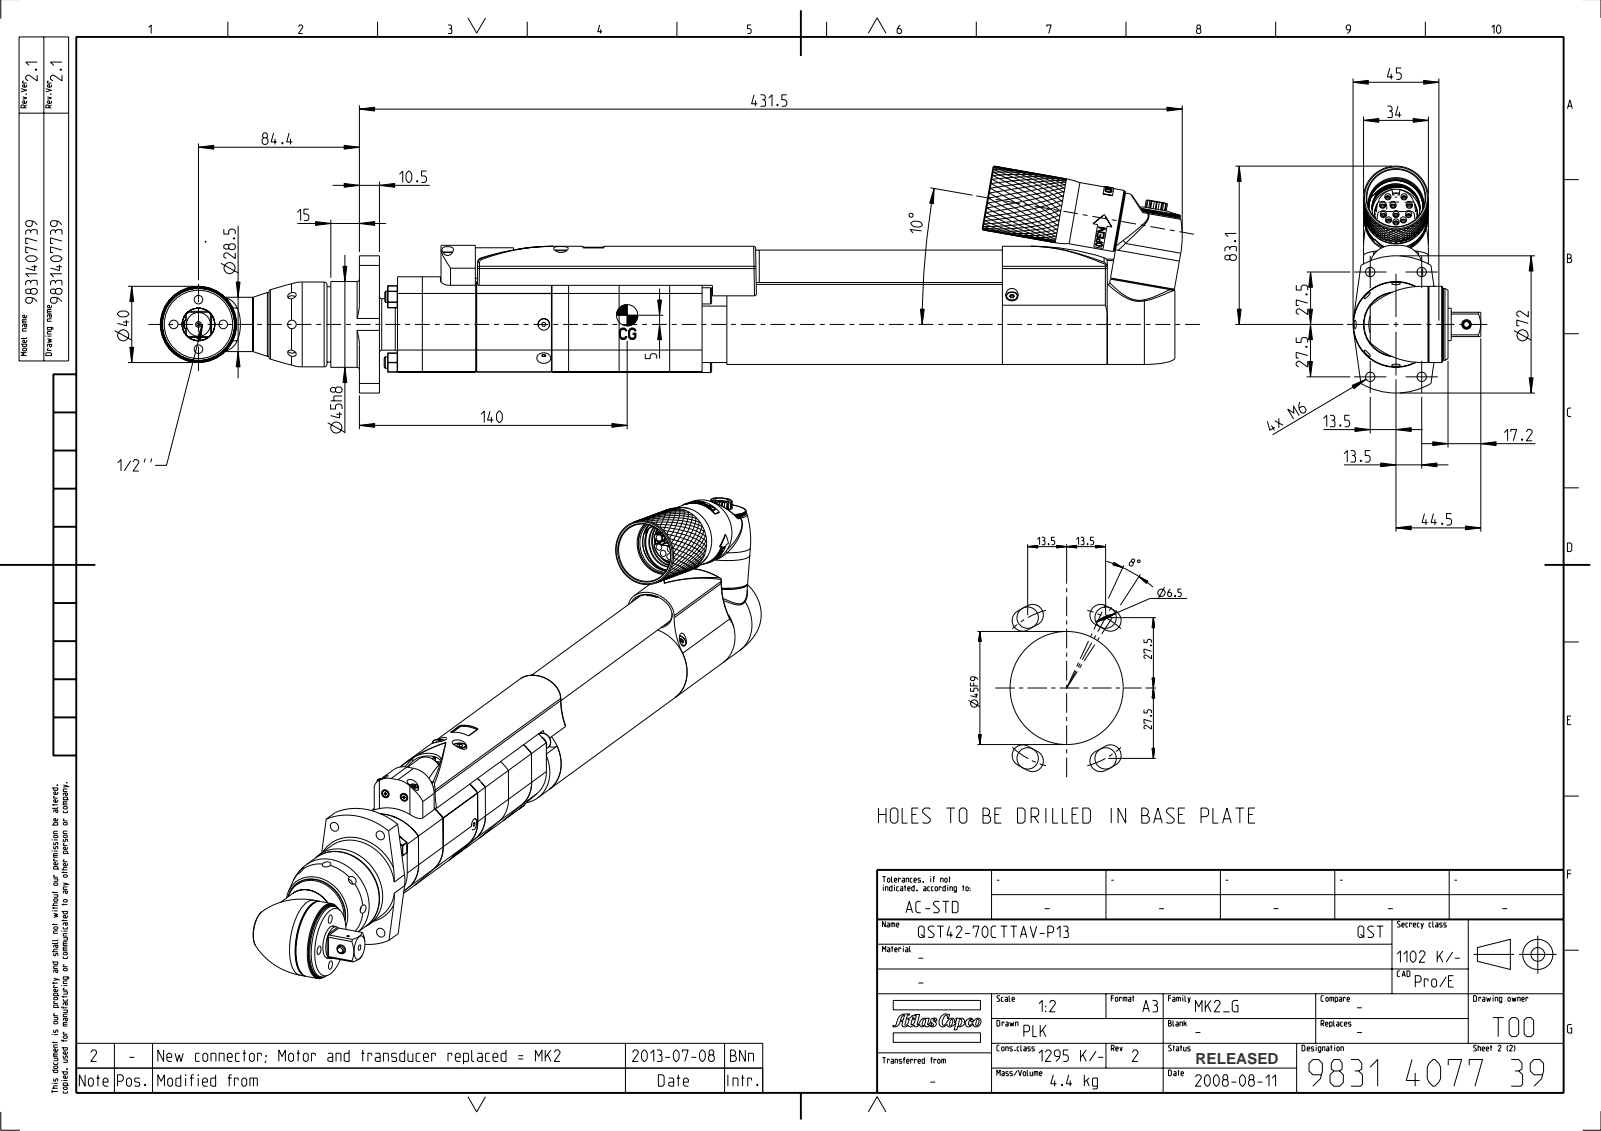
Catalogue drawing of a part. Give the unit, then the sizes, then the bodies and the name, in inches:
Units: inches
Overall size (bounding box): 21.099 × 4.687 × 2.638
Round holes (diameter × count): ⌀0.104 ×11, ⌀0.129 ×11, ⌀0.142 ×11, ⌀0.177 ×10, ⌀0.13 ×9, ⌀0.097 ×5, ⌀0.128 ×5, ⌀0.194 ×5, ⌀0.076 ×4, ⌀0.055 ×3, ⌀0.059 ×3, ⌀0.116 ×3
Round bosses / shafts (diameter × count): ⌀0.236 ×11, ⌀0.118 ×9, ⌀0.157 ×6, ⌀1.339 ×4, ⌀0.197 ×4, ⌀0.335 ×3, ⌀0.098 ×3, ⌀1.181 ×2
Partial cylindrical surfaces — rounded edges, fillets, slot ends (radius × count): R0.039 ×79, R0.008 ×64, R0.004 ×53, R0.02 ×21, R0.011 ×12, R0.02 ×12, R0.079 ×9, R0.098 ×8
Main face-to-face distances: 1.496, 0.138, 0.374, 0.748, 0.512, 0.886, 1.043, 7.173, 0.413, 6.287
Hole centre spacings: 0.282, 0.292, 0.627, 0.289, 0.591, 1.378, 0.217, 0.292
Volume: 30.24 in³ · Surface area: 461.8 in²
Bodies: 50 solids, 5203 faces (2157 planar, 1650 cylindrical, 1396 other)
Part name (STEP PRODUCT): 4230260102; 4230260112_ASM; 4230262500; 0219110017 (+8 more)
STEP written by: CREO PARAMETRIC BY PTC INC, 2015380 (CONFIG_CONTROL_DESIGN)
